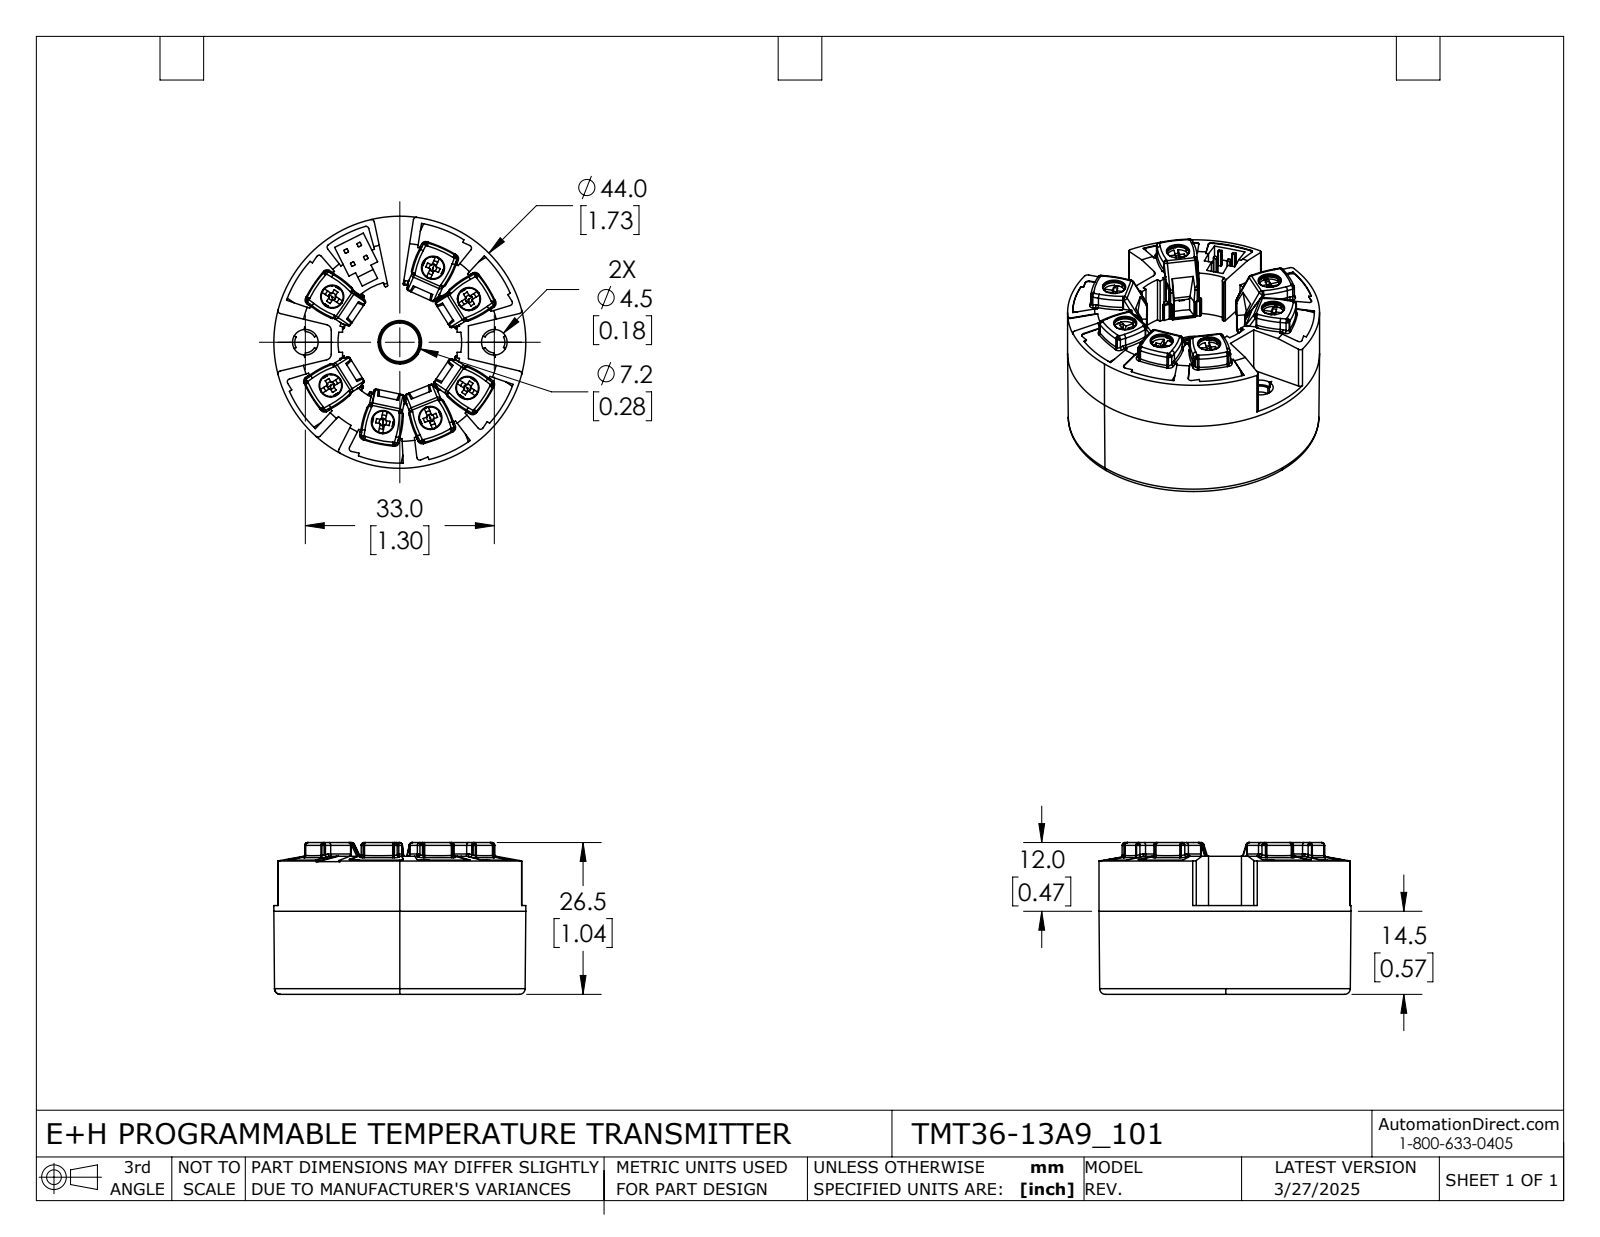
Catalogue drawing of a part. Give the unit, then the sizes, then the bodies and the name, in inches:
Units: inches
Overall size (bounding box): 1.732 × 1.732 × 1.043
Round holes (diameter × count): ⌀0.159 ×7, ⌀0.176 ×2, ⌀0.265 ×1, ⌀0.283 ×1
Round bosses / shafts (diameter × count): ⌀0.156 ×7, ⌀0.151 ×7, ⌀1.732 ×1
Partial cylindrical surfaces — rounded edges, fillets, slot ends (radius × count): R0.02 ×148, R0.008 ×110, R0.012 ×68, R0.01 ×42, R0.004 ×16, R0.592 ×14, R0.039 ×9, R0.711 ×7
Main face-to-face distances: 0.61, 0.949, 0.339, 0.094, 0.433, 1.043, 0.03, 0.203, 1.003, 0.393
Hole centre spacings: 0.561, 0.328, 0.344, 0.364, 0.561, 0.611, 0.65, 0.859
Volume: 1.894 in³ · Surface area: 14.22 in²
Bodies: 1 solid, 1795 faces (617 planar, 665 cylindrical, 513 other)
Part name (STEP PRODUCT): TMT36-13A9_101
STEP written by: SolidWorks 2024 (AUTOMOTIVE_DESIGN)
